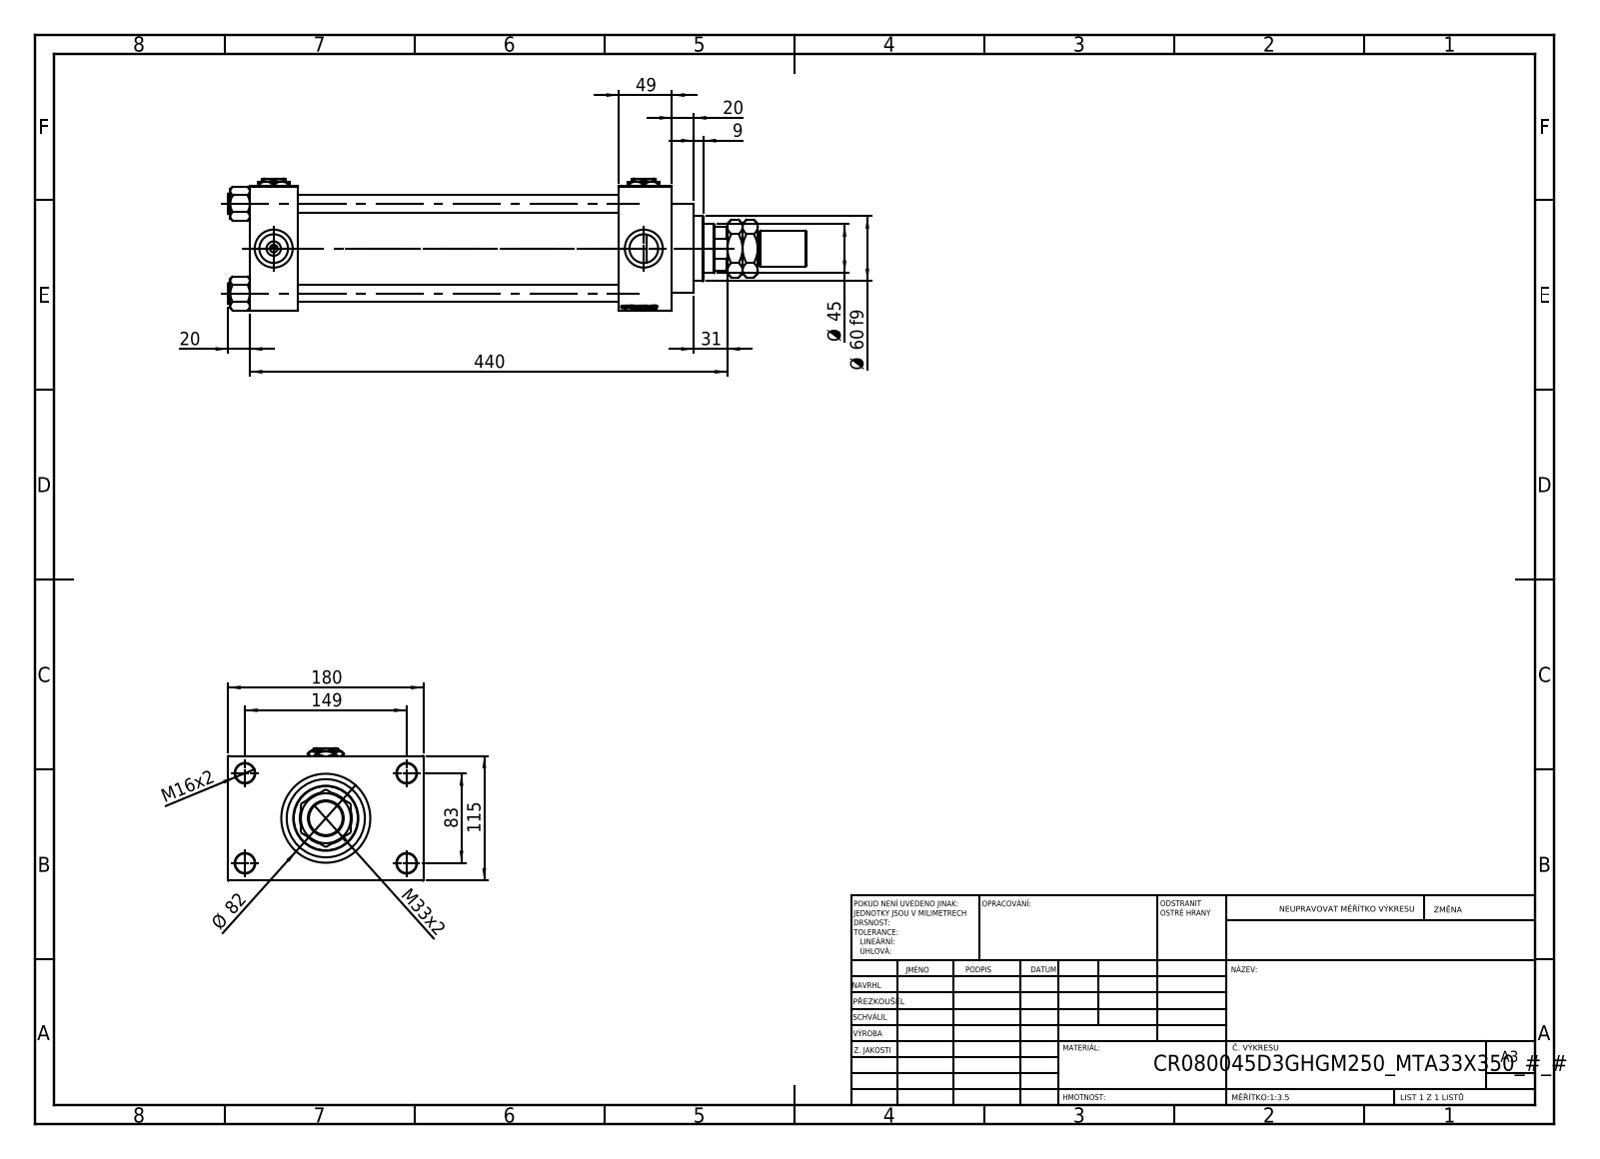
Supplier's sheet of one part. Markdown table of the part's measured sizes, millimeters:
| quantity | value |
| --- | --- |
| part name | V215CR_VCP_D; V215_VC_A; MTA; V215CR_D_Body (+3 more) |
| STEP written by | SolidWorks 2019 (CONFIG_CONTROL_DESIGN) |
| units | millimeters |
| bodies | 14 solids, 1301 faces (608 planar, 103 cylindrical, 590 other) |
| overall size | 533 × 180 × 122 |
| volume | 2 810 000 mm³ |
| surface area | 520 526 mm² |
| round holes (diameter × count) | 16 × 4, 18 × 4, 26.44 × 4, 35 × 4, 7 × 3, 31.5 × 1, 45 × 1, 48 × 1, 61 × 1, 72 × 1, 80 × 1 |
| round bosses / shafts (diameter × count) | 19 × 4, 86 × 1, 82 × 1, 60 × 1, 33 × 1, 31 × 1 |
| partial cylindrical surfaces (radius × count) | 22 × 1 |
| main face-to-face distances | 115, 296, 345, 49, 44, 340, 389, 32.5, 147.5, 46 |
| hole center spacings | 33.15, 58.48, 82.7, 85.28, 89.24, 115.85, 142.43, 83 |
